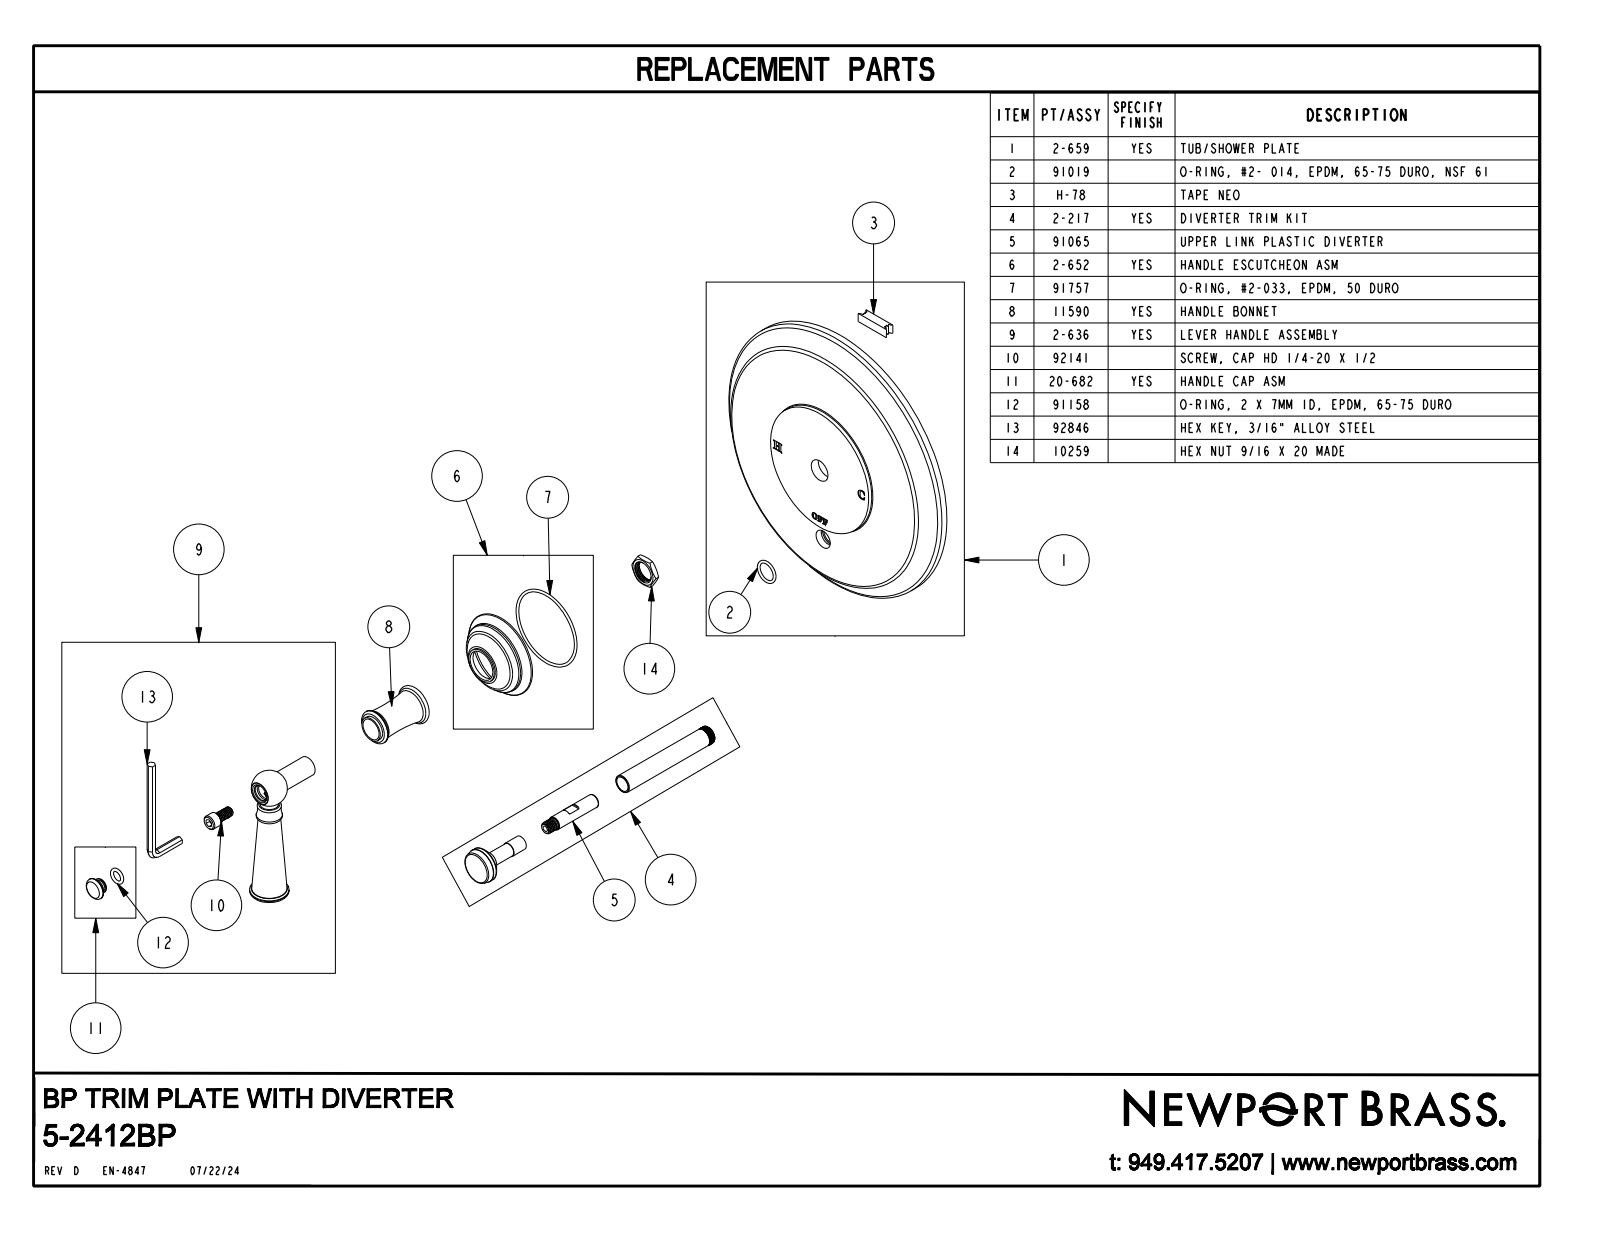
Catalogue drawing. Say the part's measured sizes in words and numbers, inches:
The part is named "5-2412BP". Its 3-D file was written by "CREO PARAMETRIC BY PTC INC, 2018400 (CONFIG_CONTROL_DESIGN)". It is 1 solid with 231 faces: 42 planar, 20 cylindrical and 169 other. Overall it measures 7.5 by 7.5 by 4.072 inches. Its volume is 30.2 cubic inches and its surface area 117.3 square inches. Round bosses or shafts: 2 of diameter 0.9, 1 of diameter 7.5, 1 of diameter 0.983, 1 of diameter 0.649, 1 of diameter 0.56, 1 of diameter 0.517, 1 of diameter 0.472, 1 of diameter 0.461. The main face-to-face distances are 0.625, 0.75, 0.125, 1.977, 1.352, 1.227, 2.89, 2.265, 2.14, 0.913.
